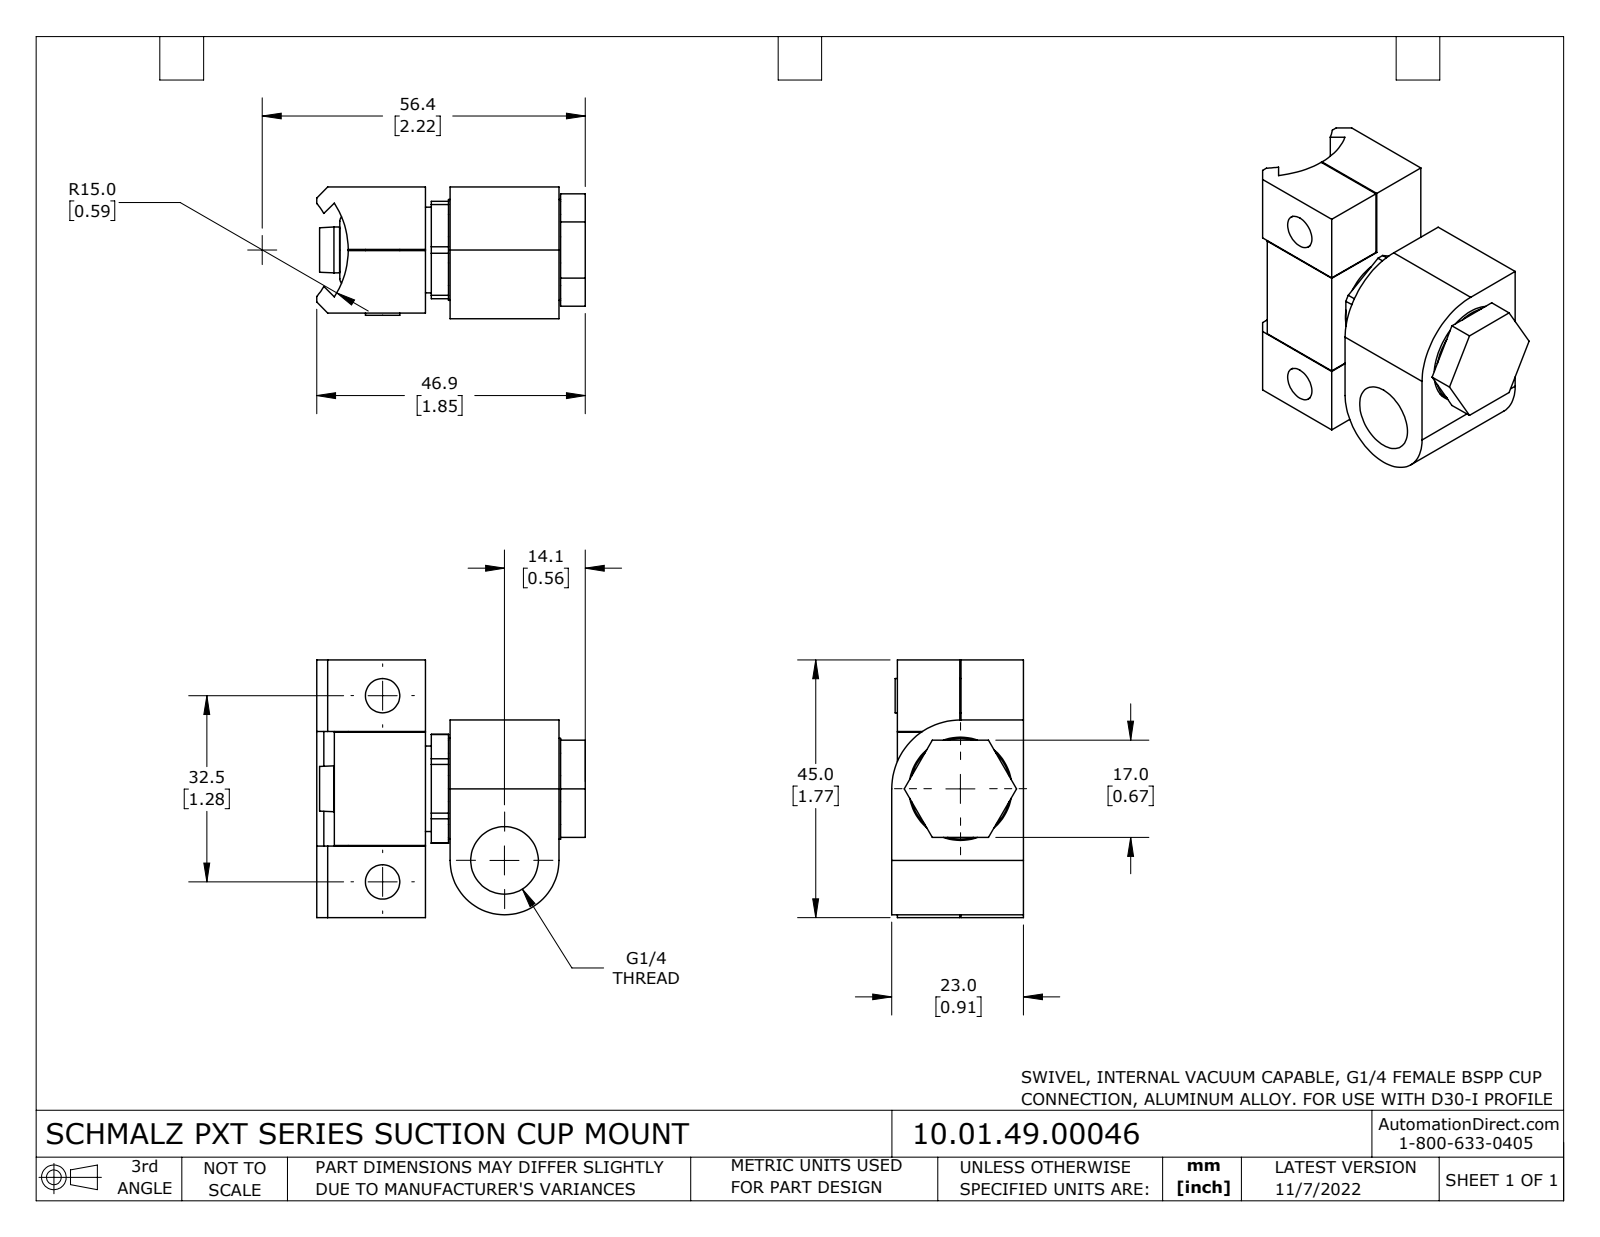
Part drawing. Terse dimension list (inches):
name: 10.01.49.00046
written by: SolidWorks 2021 (CONFIG_CONTROL_DESIGN)
unit: in
bodies: 9 solids, 163 faces (85 planar, 64 cylindrical, 14 other)
size: 1.846 × 1.772 × 0.906
volume: 1.732 in³; area: 27.01 in²
holes: 2× ⌀0.197, 2× ⌀0.26, 2× ⌀0.433, 2× ⌀0.465, 1× ⌀0.52, 1× ⌀0.6, 1× ⌀0.709
bosses: 2× ⌀0.394, 2× ⌀0.236, 1× ⌀0.693, 1× ⌀0.656, 1× ⌀0.589, 1× ⌀0.518, 1× ⌀0.315, 1× ⌀0.295
rounds: 2× R0.374, 1× R0.472, 1× R0.492, 1× R0.591
face distances: 0.866, 0.437, 0.429, 0.252, 0.496, 0.413, 0.783, 0.748, 0.917, 0.039
hole spacings: 0.852, 1.28, 1.409
